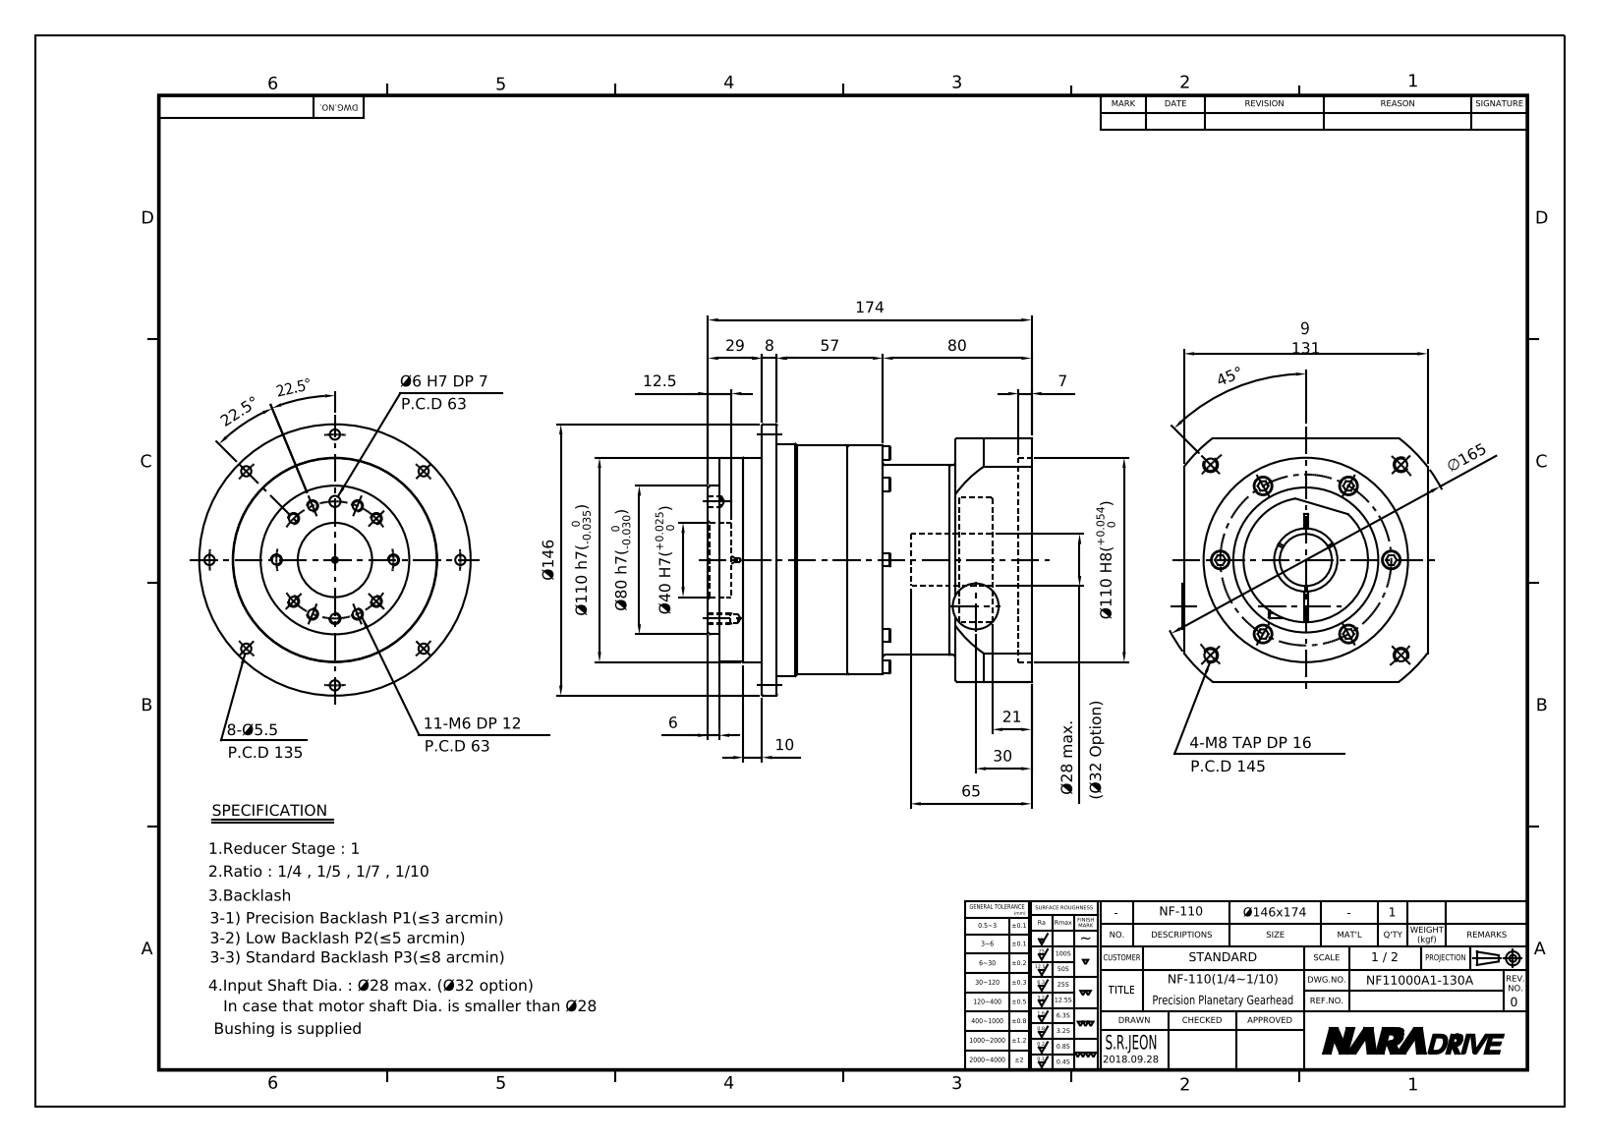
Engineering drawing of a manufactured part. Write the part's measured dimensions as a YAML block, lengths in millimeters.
part_name: "NF11000A1-130A"
step_written_by: "Autodesk Inventor 2015 (AUTOMOTIVE_DESIGN)"
units: millimeters
bodies: {solids: 1, faces: 475, planar: 205, cylindrical: 139, other: 131}
overall_size: [174, 146, 146]
volume: 1468000
surface_area: 211426
round_holes:
  - {diameter: 4.92, count: 17}
  - {diameter: 3.24, count: 8}
  - {diameter: 4.6, count: 8}
  - {diameter: 5.5, count: 8}
  - {diameter: 6.6, count: 6}
  - {diameter: 11, count: 6}
  - {diameter: 6.65, count: 5}
  - {diameter: 2, count: 1}
  - {diameter: 6, count: 1}
  - {diameter: 7, count: 1}
  - {diameter: 9, count: 1}
  - {diameter: 14.5, count: 1}
round_bosses_or_shafts:
  - {diameter: 7, count: 8}
  - {diameter: 4, count: 8}
  - {diameter: 10, count: 6}
  - {diameter: 6, count: 6}
  - {diameter: 8, count: 2}
  - {diameter: 146, count: 1}
  - {diameter: 125, count: 1}
  - {diameter: 123, count: 1}
partial_cylinders:
  - {radius: 0.5, count: 4}
  - {radius: 1, count: 4}
  - {radius: 7, count: 1}
  - {radius: 82.5, count: 1}
face_to_face_distances: [8, 96, 41, 104, 131, 38, 88, 46, 58, 145]
hole_center_spacings: [74.49, 50.41, 67.5, 92.5, 31.5, 46, 51.66, 95.46]
